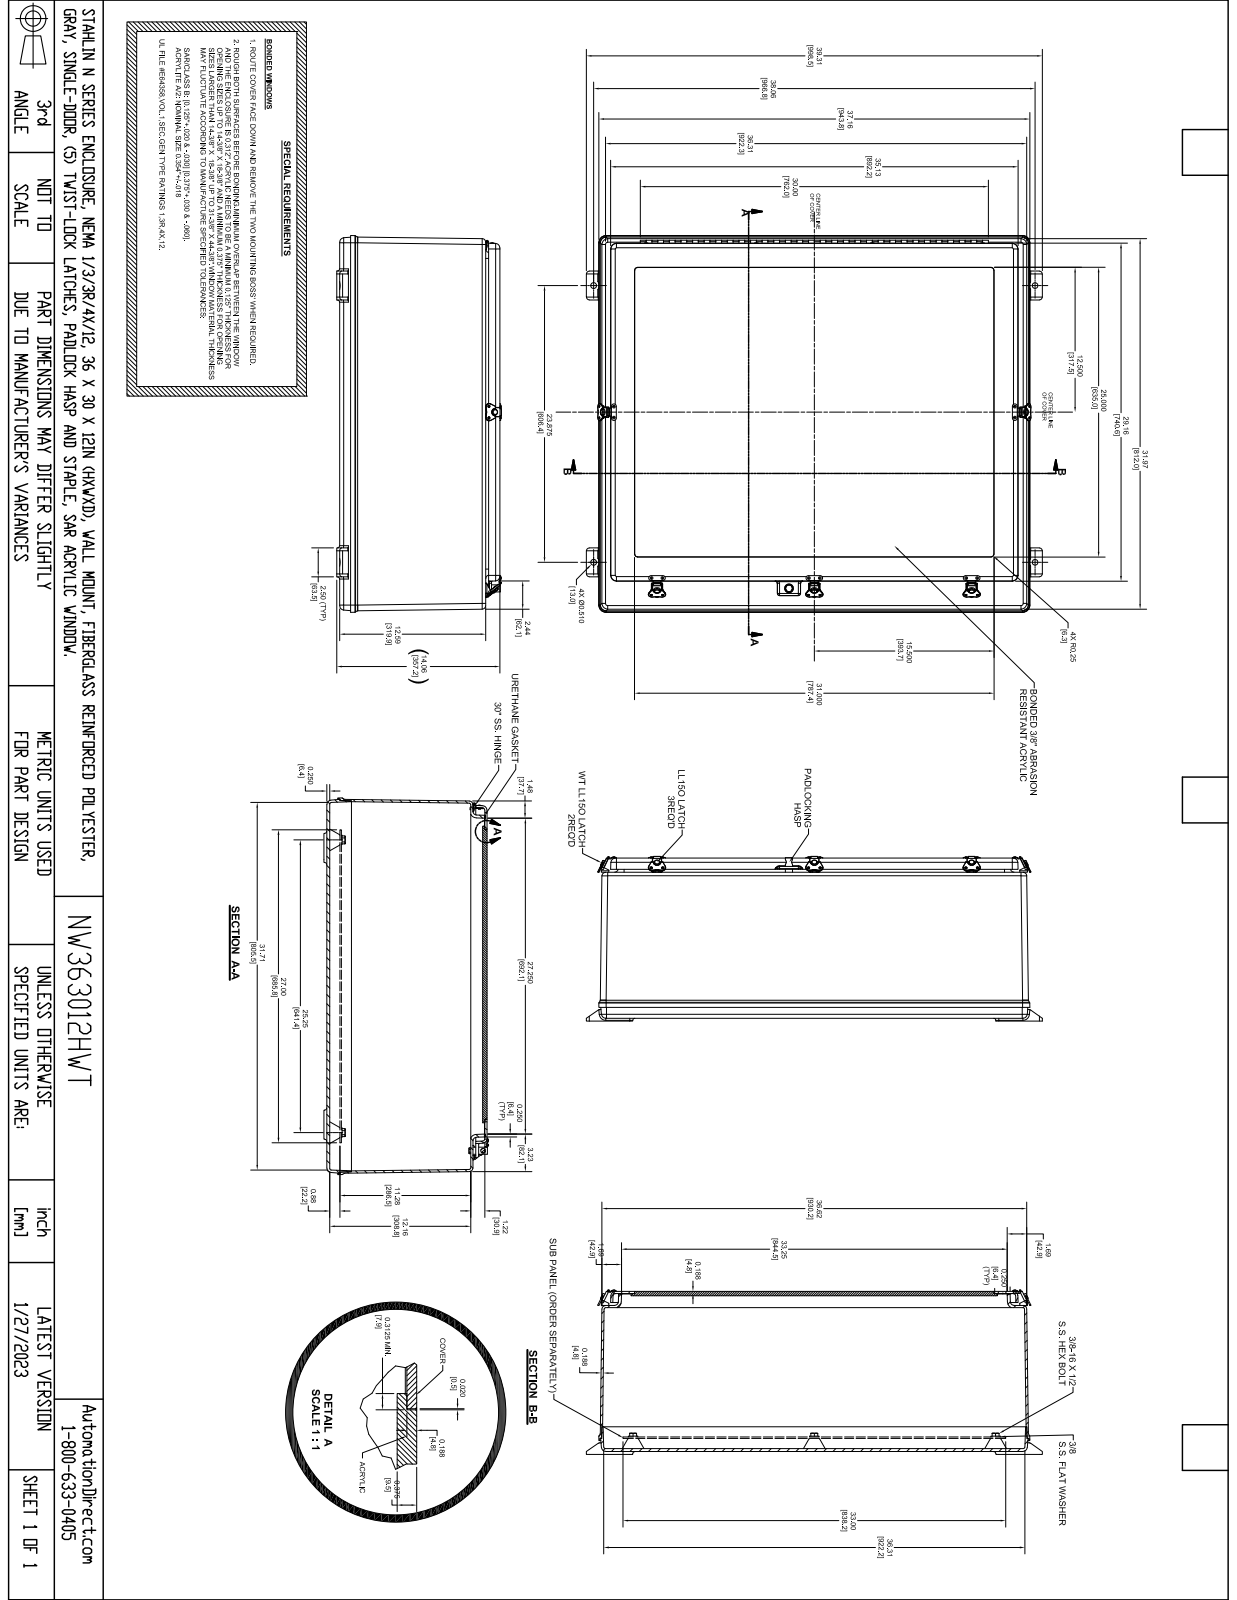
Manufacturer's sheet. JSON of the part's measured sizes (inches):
{"part_name": "TW363012HWT", "step_written_by": "SolidWorks 2018 (AUTOMOTIVE_DESIGN)", "units": "inches", "bodies": {"solids": 70, "faces": 1944, "planar": 736, "cylindrical": 760, "other": 448}, "overall_size": [39.313, 32.5, 14.212], "volume_in3": 1078, "surface_area_in2": 9500, "round_holes": [[0.13, 36], [0.063, 20], [0.138, 10], [0.187, 10], [0.065, 6], [0.307, 6], [0.563, 4], [0.156, 3], [0.065, 2], [0.135, 2], [0.433, 2], [0.5, 2]], "round_bosses_or_shafts": [[0.14, 20], [0.297, 8], [0.5, 5], [0.2, 3], [0.563, 2], [0.25, 1], [0.201, 1]], "partial_cylinders_radius": [[0.01, 127], [0.25, 28], [0.312, 23], [0.03, 20], [0.188, 14], [0.375, 13], [0.5, 12], [0.125, 10]], "face_to_face_distances": [0.25, 0.188, 13.817, 13.567, 13.442, 13.192, 0.375, 0.187, 1.223, 0.187], "hole_center_spacings": [13.563, 9.5, 19.5, 0.794, 1, 1.468, 3.474, 13.583]}
